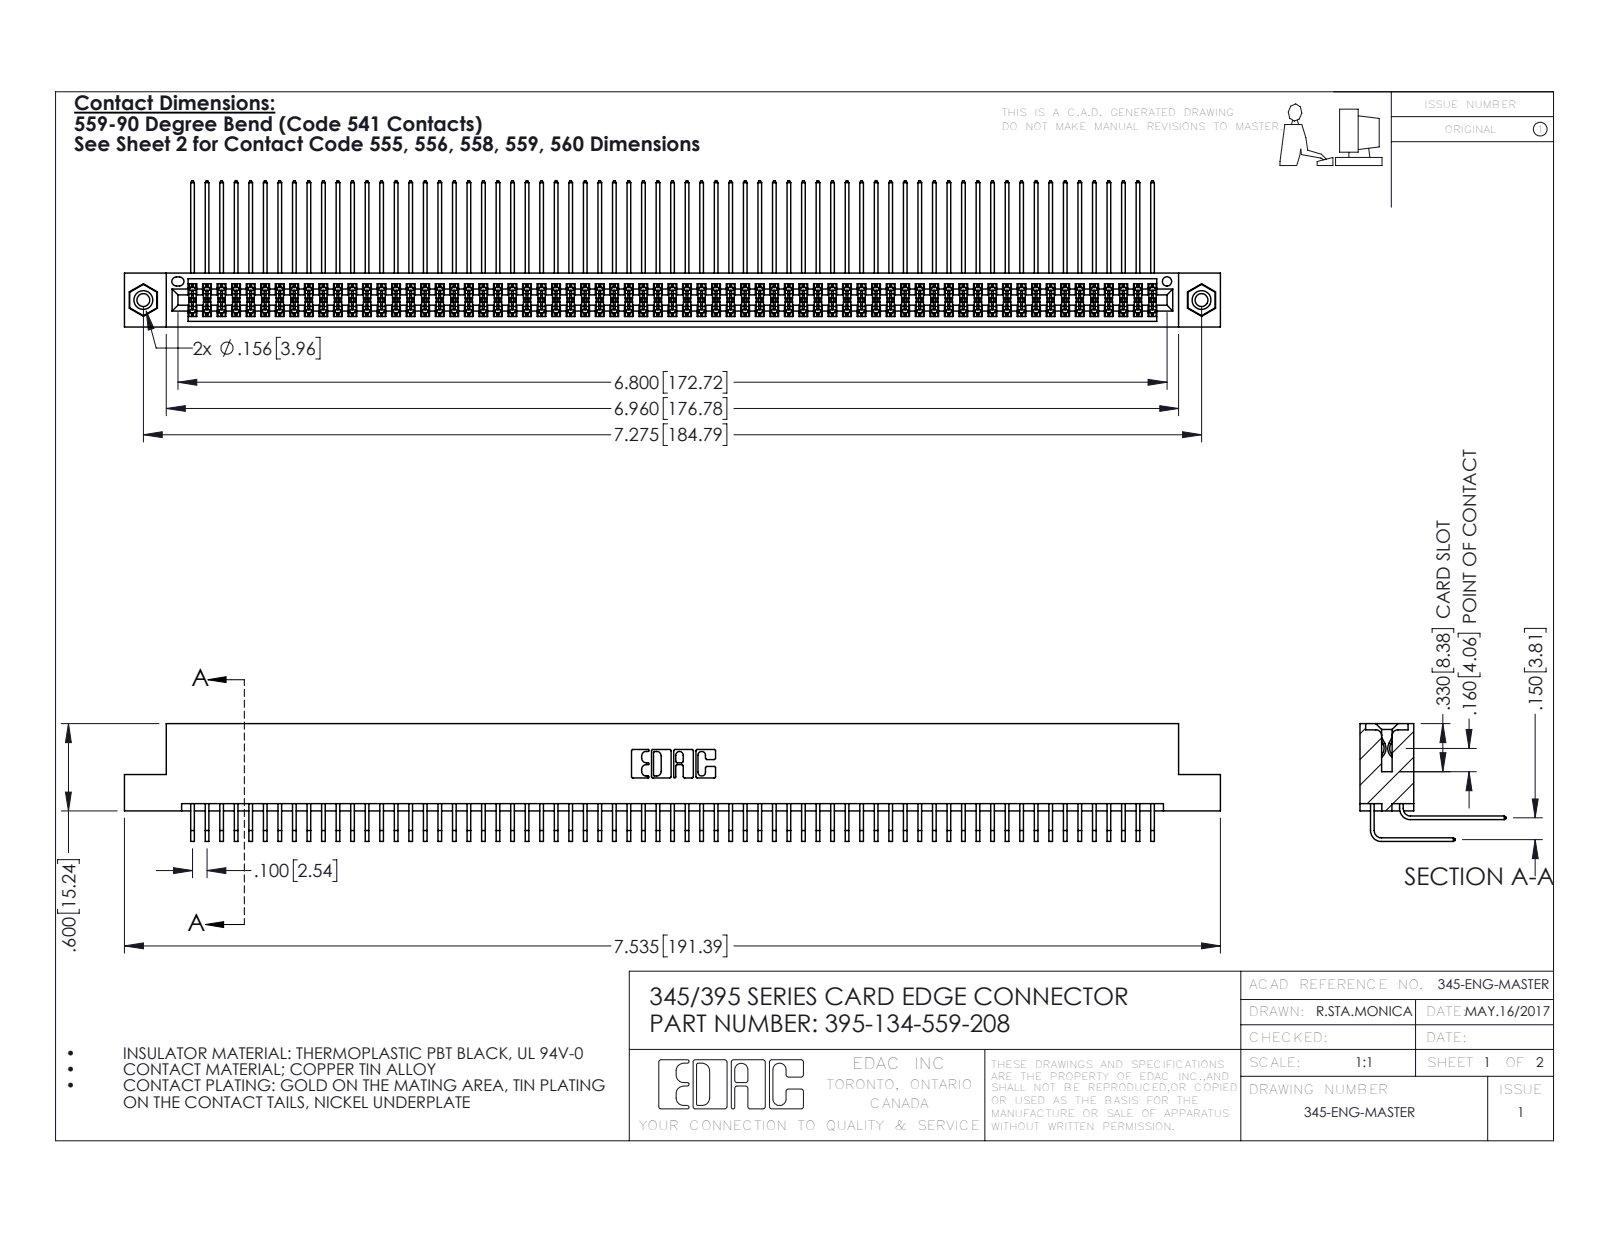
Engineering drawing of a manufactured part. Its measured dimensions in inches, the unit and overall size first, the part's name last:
Units: inches
Overall size (bounding box): 7.535 × 1.005 × 0.809
Round holes (diameter × count): ⌀0.089 ×2, ⌀0.125 ×2, ⌀0.156 ×2, ⌀0.064 ×1
Round bosses / shafts (diameter × count): ⌀0.155 ×2
Partial cylindrical surfaces — rounded edges, fillets, slot ends (radius × count): R0.006 ×202, R0.01 ×22, R0.007 ×6, R0.031 ×6, R0.026 ×3, R0.014 ×2, R0.019 ×2, R0.022 ×2
Main face-to-face distances: 0.072, 0.298, 0.2, 0.37, 0.098, 0.272, 0.025, 0.225, 0.175, 0.15
Hole centre spacings: 0.27, 7.039, 7.275
Volume: 1.195 in³ · Surface area: 51.29 in²
Bodies: 137 solids, 7154 faces (4802 planar, 2336 cylindrical, 16 other)
Part name (STEP PRODUCT): 345-250-001_345-250-003-102; 345 Part_Flush Mounting Lugs - 0.156 Dia-TI; 345-292-001_559 Tail - 2; 395-134-559-208 (+1 more)
STEP written by: SolidWorks 2016 (CONFIG_CONTROL_DESIGN)
